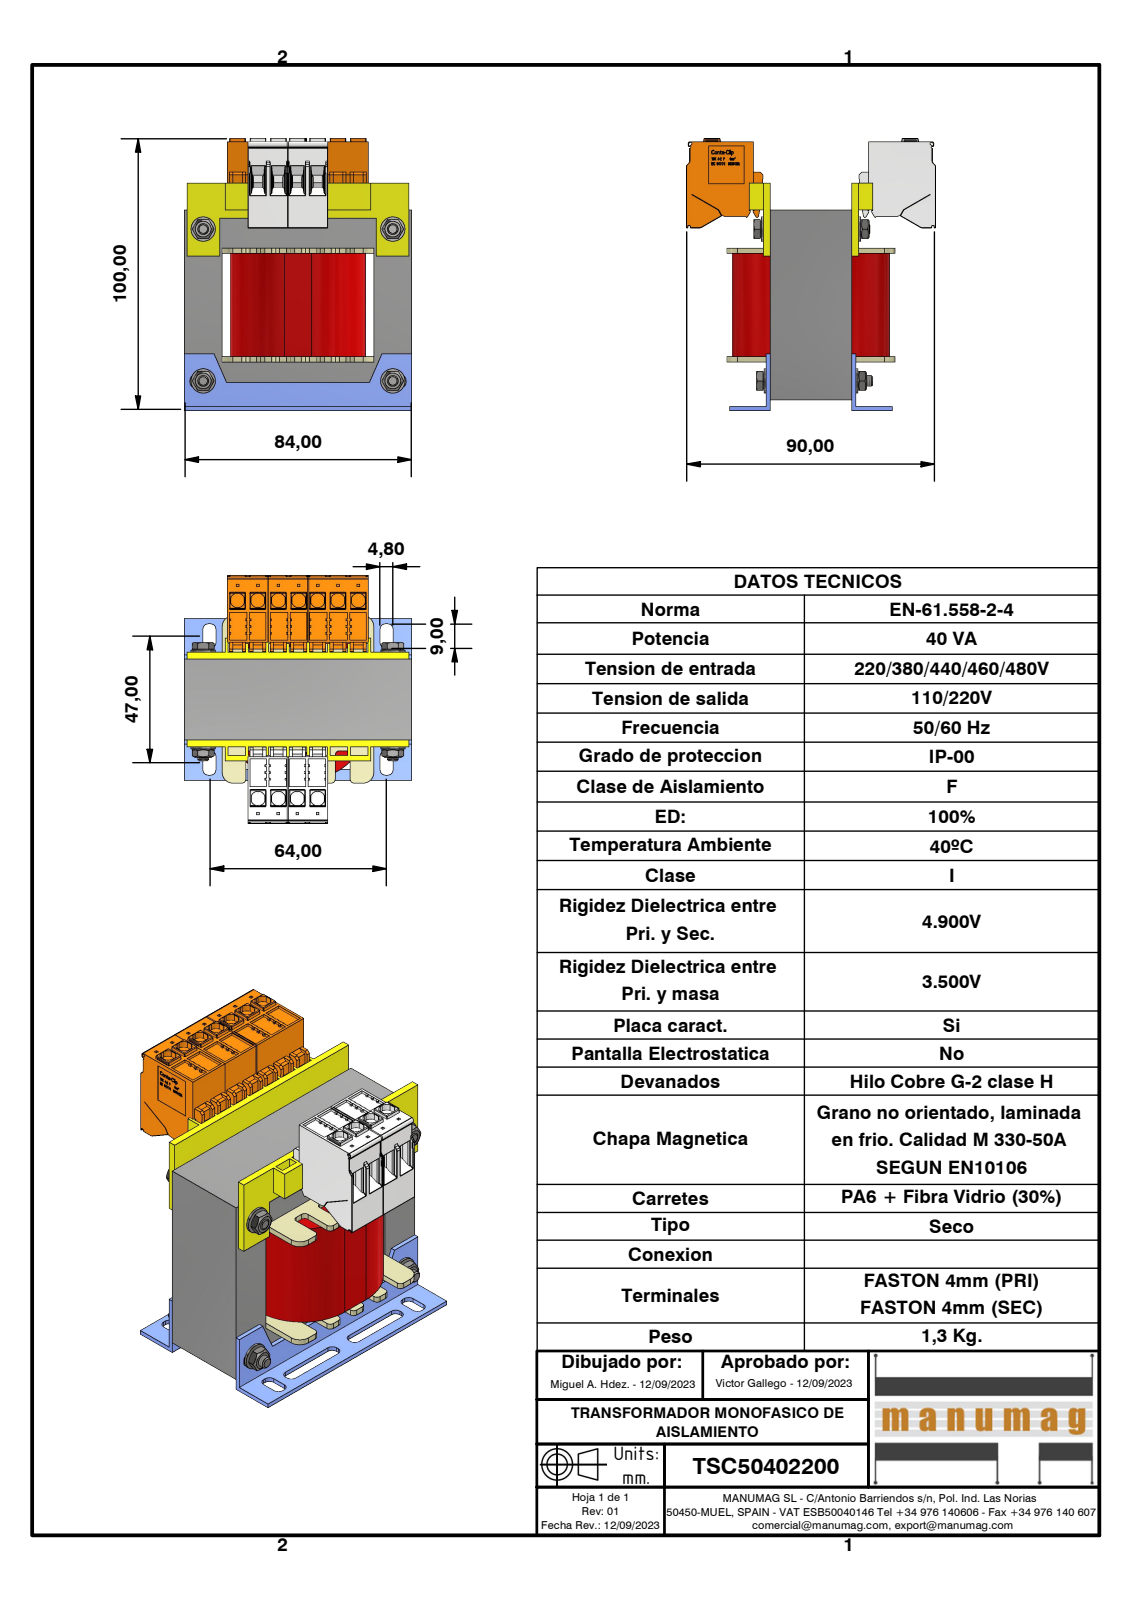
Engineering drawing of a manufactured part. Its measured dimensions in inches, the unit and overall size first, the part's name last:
Units: inches
Overall size (bounding box): 3.957 × 3.618 × 3.307
Round holes (diameter × count): ⌀0.128 ×4, ⌀0.169 ×4, ⌀0.177 ×4, ⌀0.157 ×2
Round bosses / shafts (diameter × count): ⌀0.354 ×4, ⌀0.232 ×4, ⌀0.143 ×4, ⌀0.157 ×2
Partial cylindrical surfaces — rounded edges, fillets, slot ends (radius × count): R0.006 ×431, R0.008 ×122, R0.079 ×40, R0.059 ×32, R0.02 ×30, R0.012 ×12, R0.106 ×11, R0.197 ×10
Main face-to-face distances: 0.551, 2.205, 1.181, 1.102, 1.654, 2.756, 0.059, 0.098, 0.039, 3.307
Hole centre spacings: 2.205, 2.756, 3.529
Volume: 16.85 in³ · Surface area: 160.9 in²
Bodies: 27 solids, 9110 faces (7448 planar, 1111 cylindrical, 551 other)
Part name (STEP PRODUCT): TSC50402200; EI84 x 70 - 30 (RC28); EI 84 X 70 - 30; AF28DIN (+7 more)
STEP written by: Autodesk Inventor 2023 (AUTOMOTIVE_DESIGN)
